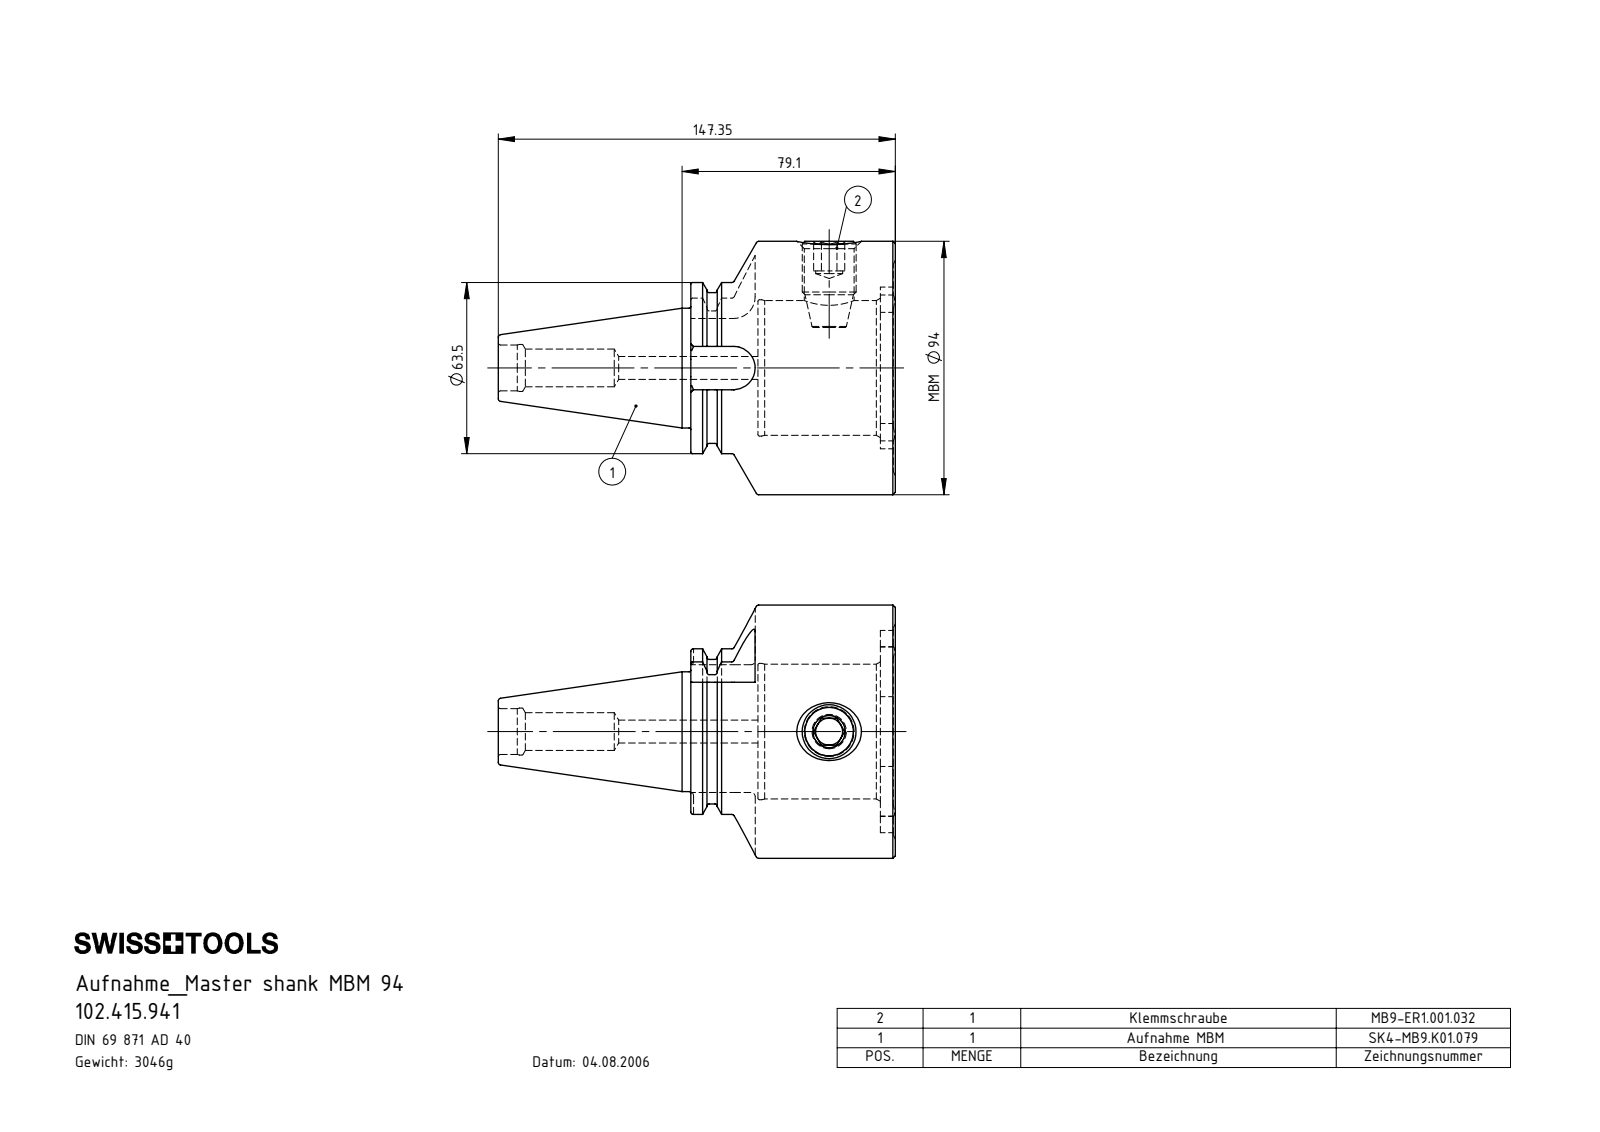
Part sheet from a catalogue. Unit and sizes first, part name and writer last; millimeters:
Units: millimetres
Overall size (bounding box): 147.35 × 94 × 94
Round holes (diameter × count): ⌀8.5 ×1, ⌀10 ×1, ⌀14 ×1, ⌀17 ×1, ⌀17.45 ×1, ⌀18.5 ×1, ⌀50 ×1, ⌀50.6 ×1
Round bosses / shafts (diameter × count): ⌀94 ×1, ⌀44.45 ×1, ⌀20 ×1
Partial cylindrical surfaces — rounded edges, fillets, slot ends (radius × count): R1.6 ×8, R5.2 ×4, R8 ×1, R8.05 ×1, R28 ×1, R30 ×1, R31.75 ×1, R37.52 ×1
Main face-to-face distances: 45.45, 51, 5.55, 24.9, 70.35, 75.9, 75.15, 50.25, 4.8, 0.75
Volume: 388 030 mm³ · Surface area: 55 458 mm²
Bodies: 2 solids, 171 faces (47 planar, 55 cylindrical, 69 other)
Part name (STEP PRODUCT): SK4-MB9.K01.079_C; MB9-ER1.001.032_A; 102.415.941
STEP written by: SolidWorks 2017 (CONFIG_CONTROL_DESIGN)
